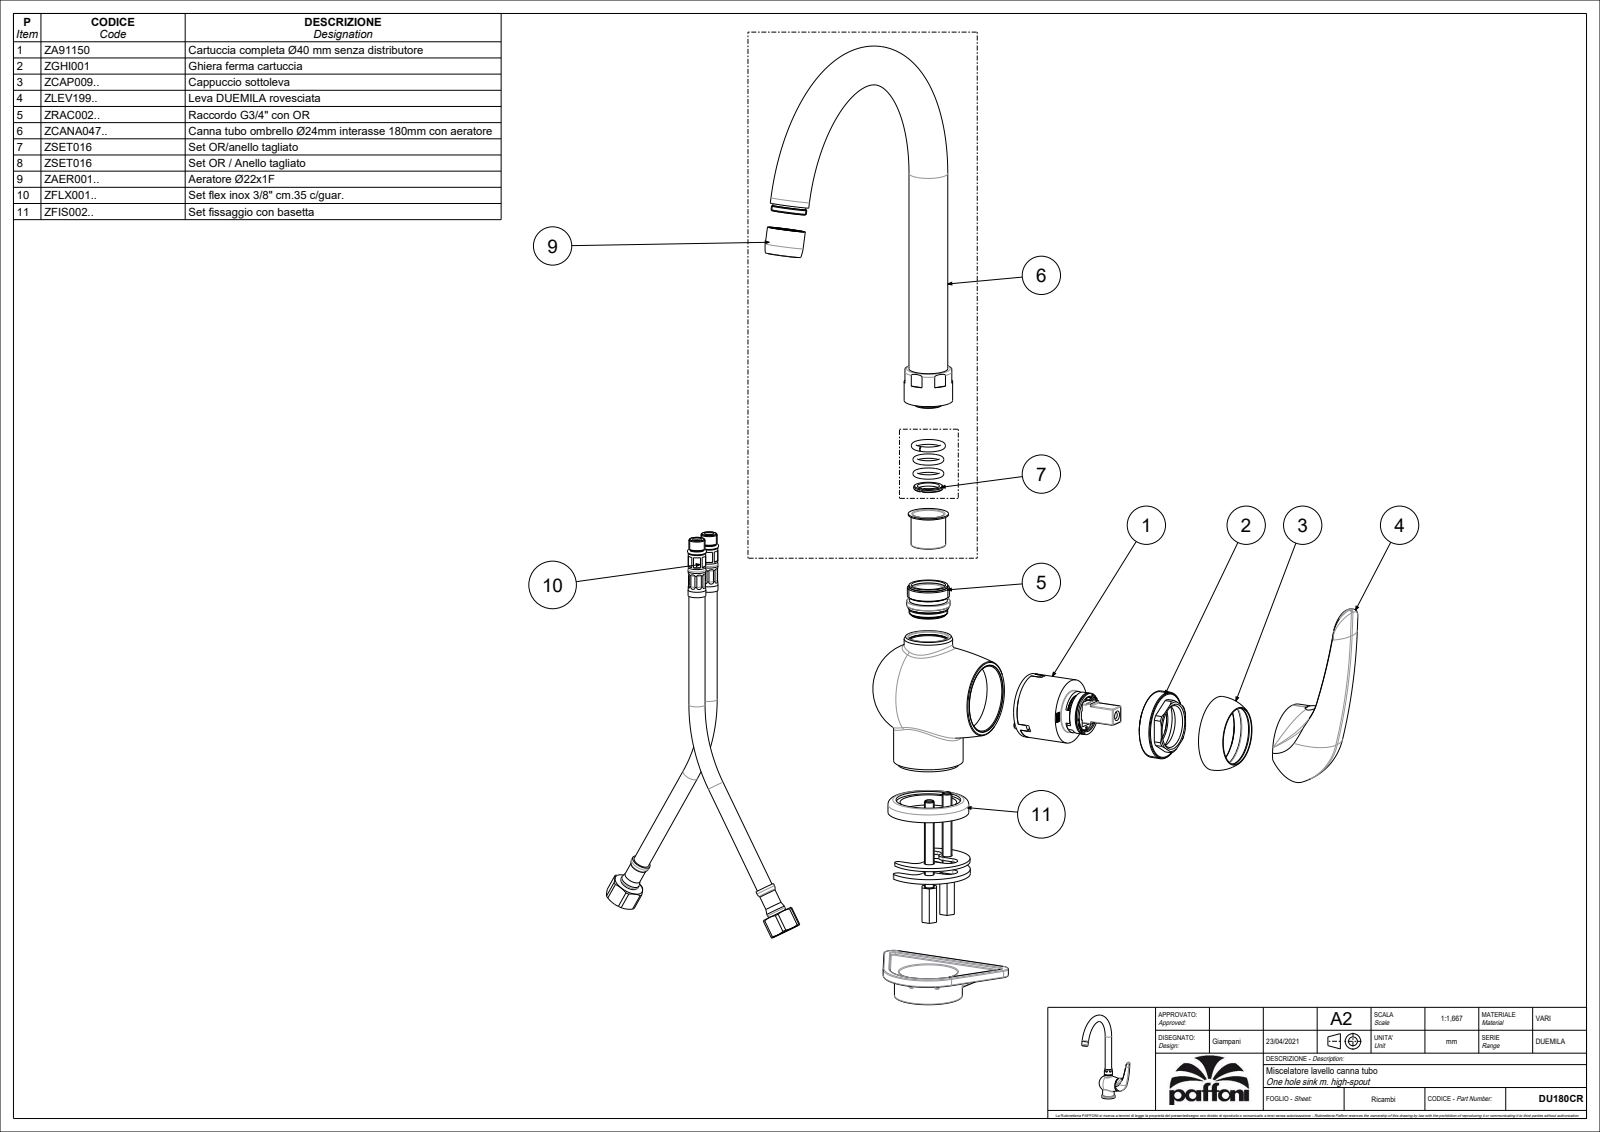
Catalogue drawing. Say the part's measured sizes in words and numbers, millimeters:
The part is named "DU180CR". Its 3-D file was written by "CREO PARAMETRIC BY PTC INC, 2020044 (CONFIG_CONTROL_DESIGN)". It is 2 solids with 229 faces: 47 planar, 79 cylindrical and 103 other. Overall it measures 333 by 215.75 by 122.95 millimeters. Its volume is 379 634 cubic millimeters and its surface area 85 209 square millimeters. Round holes: 2 of diameter 5.25, 2 of diameter 5.5, 2 of diameter 6.5, 2 of diameter 7, 2 of diameter 8, 2 of diameter 9, 2 of diameter 11, 2 of diameter 35, 1 of diameter 9.2, 1 of diameter 23, 1 of diameter 24.5, 1 of diameter 40.5. Round bosses or shafts: 2 of diameter 24, 1 of diameter 50, 1 of diameter 43, 1 of diameter 30, 1 of diameter 23.6, 1 of diameter 18.8, 1 of diameter 18.1, 1 of diameter 5. Partial cylindrical surfaces (rounded edges, fillets, slot ends): 2 of radius 1.5, 2 of radius 15, 2 of radius 24, 2 of radius 24.5, 1 of radius 18, 1 of radius 39.04, 1 of radius 340.59, 1 of radius 341.58. The main face-to-face distances are 48.47, 48.5, 88.7, 88.67, 6, 5.97, 82.7, 76.5, 76.47, 70.5. The hole center spacings are 8.6, 9.6, 12.26, 13.04, 13.46, 14.33, 15.62, 15.81.
